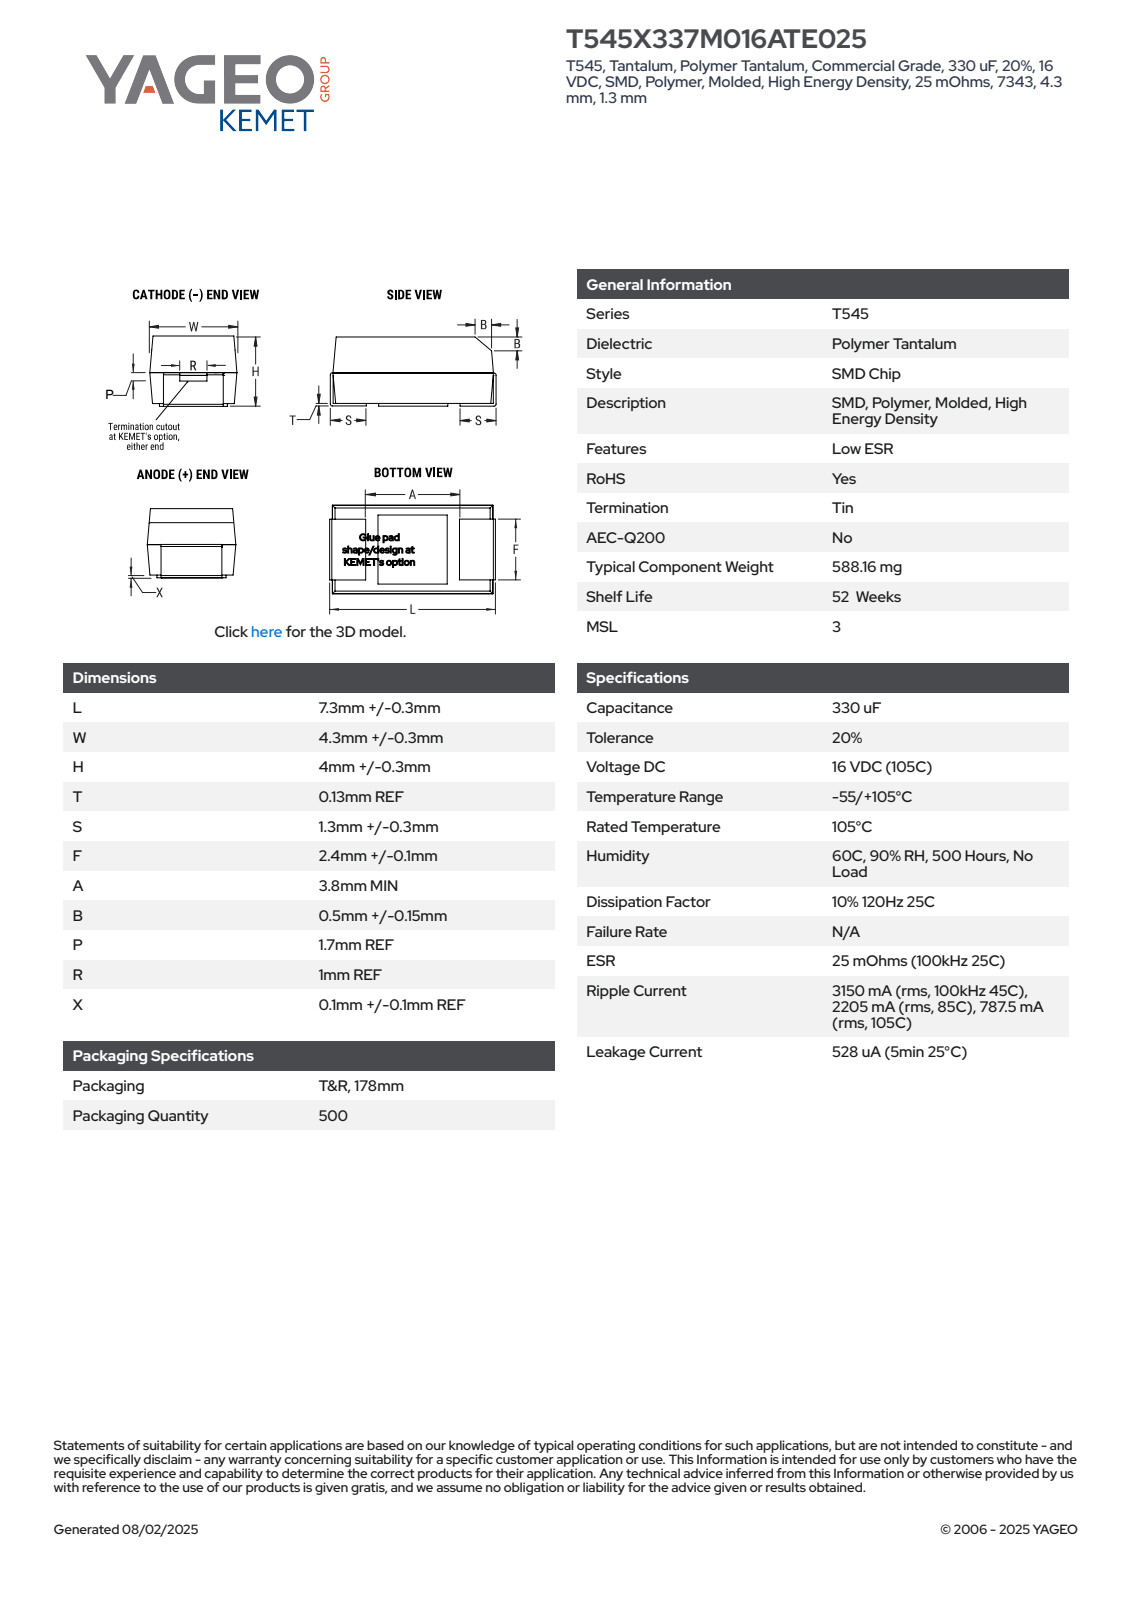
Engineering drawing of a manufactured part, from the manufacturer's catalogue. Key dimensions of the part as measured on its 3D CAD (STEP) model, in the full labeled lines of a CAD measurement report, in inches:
Part name (STEP PRODUCT): CTSM_TCM2NKKO_7343_L7.6W4.6H4.3T0.13S1.3F2.5A3.8B0.65P1.7R1X0.1
STEP written by: SolidWorks 2021 (AUTOMOTIVE_DESIGN)
Units: inches
Bodies: 4 solids, 100 faces (95 planar, 5 cylindrical, 0 other)
Overall size (bounding box): 0.299 × 0.181 × 0.17
Volume: 0.008 in³ · Surface area: 0.274 in²
Partial cylindrical surfaces — rounded edges, fillets, slot ends (radius × count): R0.004 ×4
Main face-to-face distances: 0.18, 0.165, 0.169, 0.294, 0.17, 0.299, 0.289, 0.098, 0.094, 0.205
